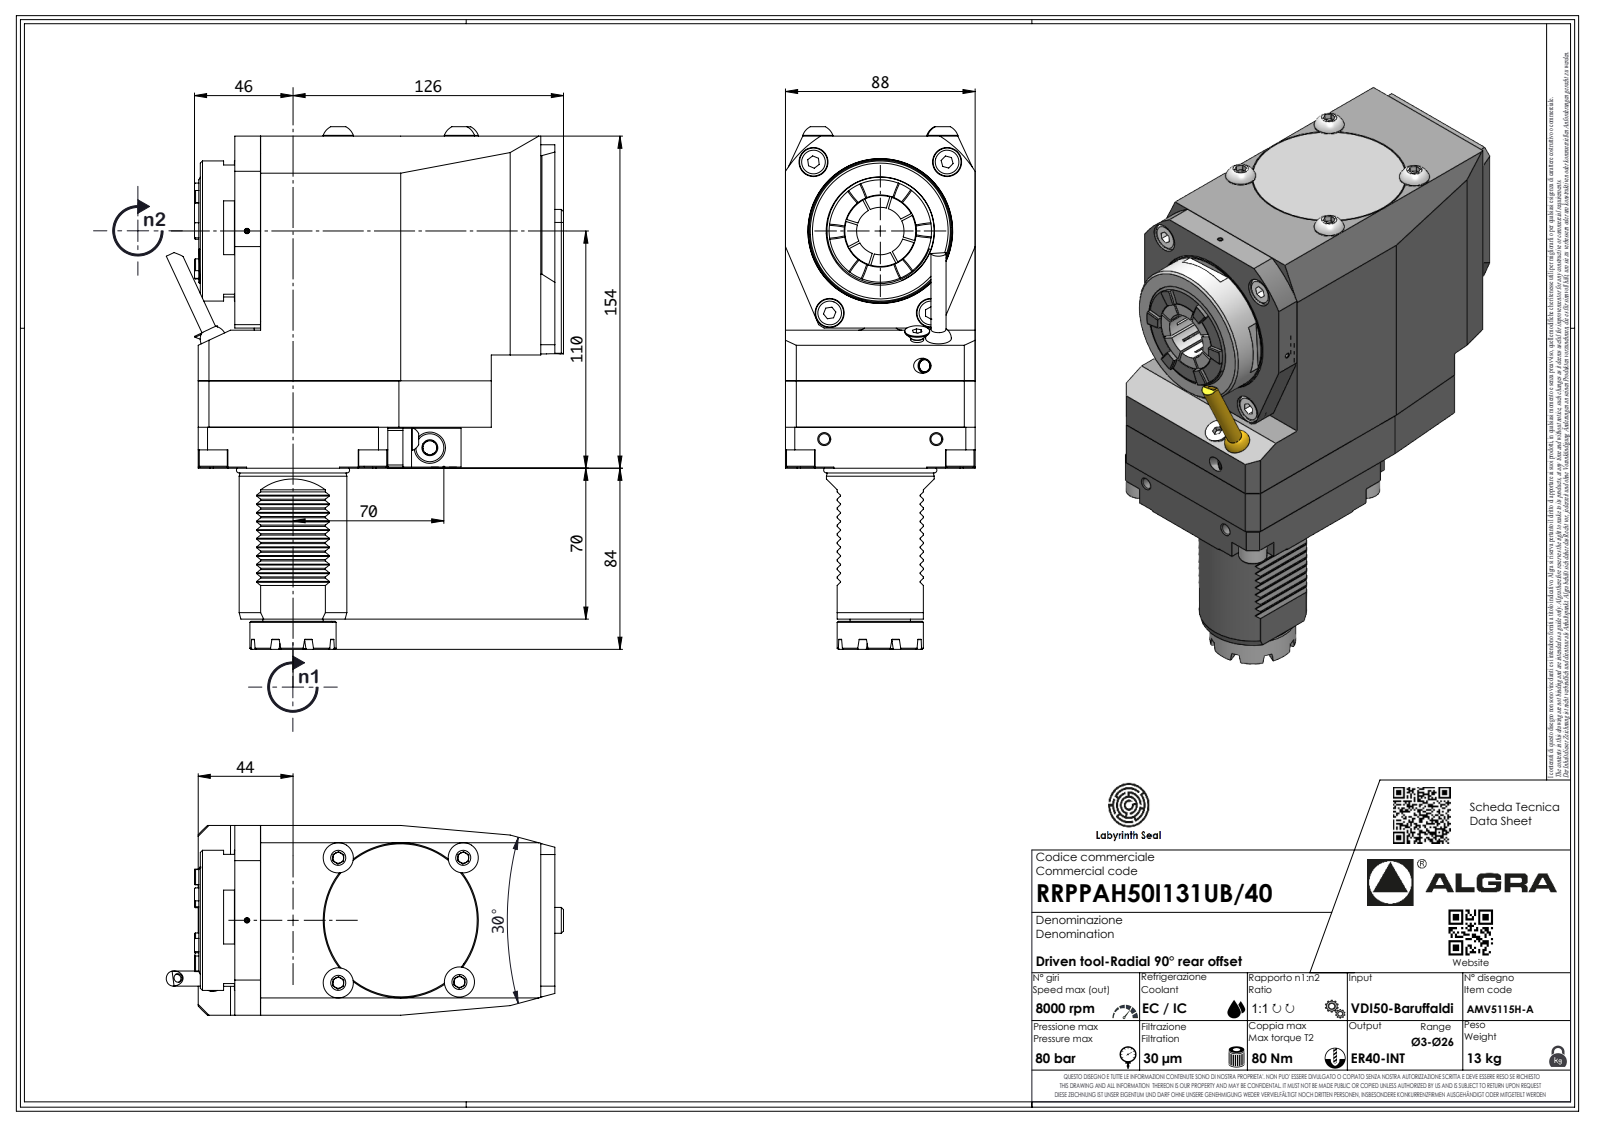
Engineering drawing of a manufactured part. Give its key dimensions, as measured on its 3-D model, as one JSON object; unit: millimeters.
{"part_name": "RRPPAH50I131UB40", "step_written_by": "SolidWorks 2023 (AUTOMOTIVE_DESIGN)", "units": "millimeters", "bodies": {"solids": 1, "faces": 695, "planar": 463, "cylindrical": 115, "other": 117}, "overall_size": [242.4, 184.32, 88], "volume_mm3": 2019000, "surface_area_mm2": 121081, "round_holes": [[2.1, 1], [10, 1]], "round_bosses_or_shafts": [[14, 4], [13, 4], [65, 1], [50, 1], [48.7, 1], [40, 1], [28, 1], [7, 1]], "partial_cylinders_radius": [[0.3, 22], [0.2, 16], [0.33, 7], [0.52, 7], [3.7, 7], [1, 4], [6.75, 4], [4, 2]], "face_to_face_distances": [88, 135, 154, 1, 165.5, 19, 0.5, 17, 148.5, 18.5]}
